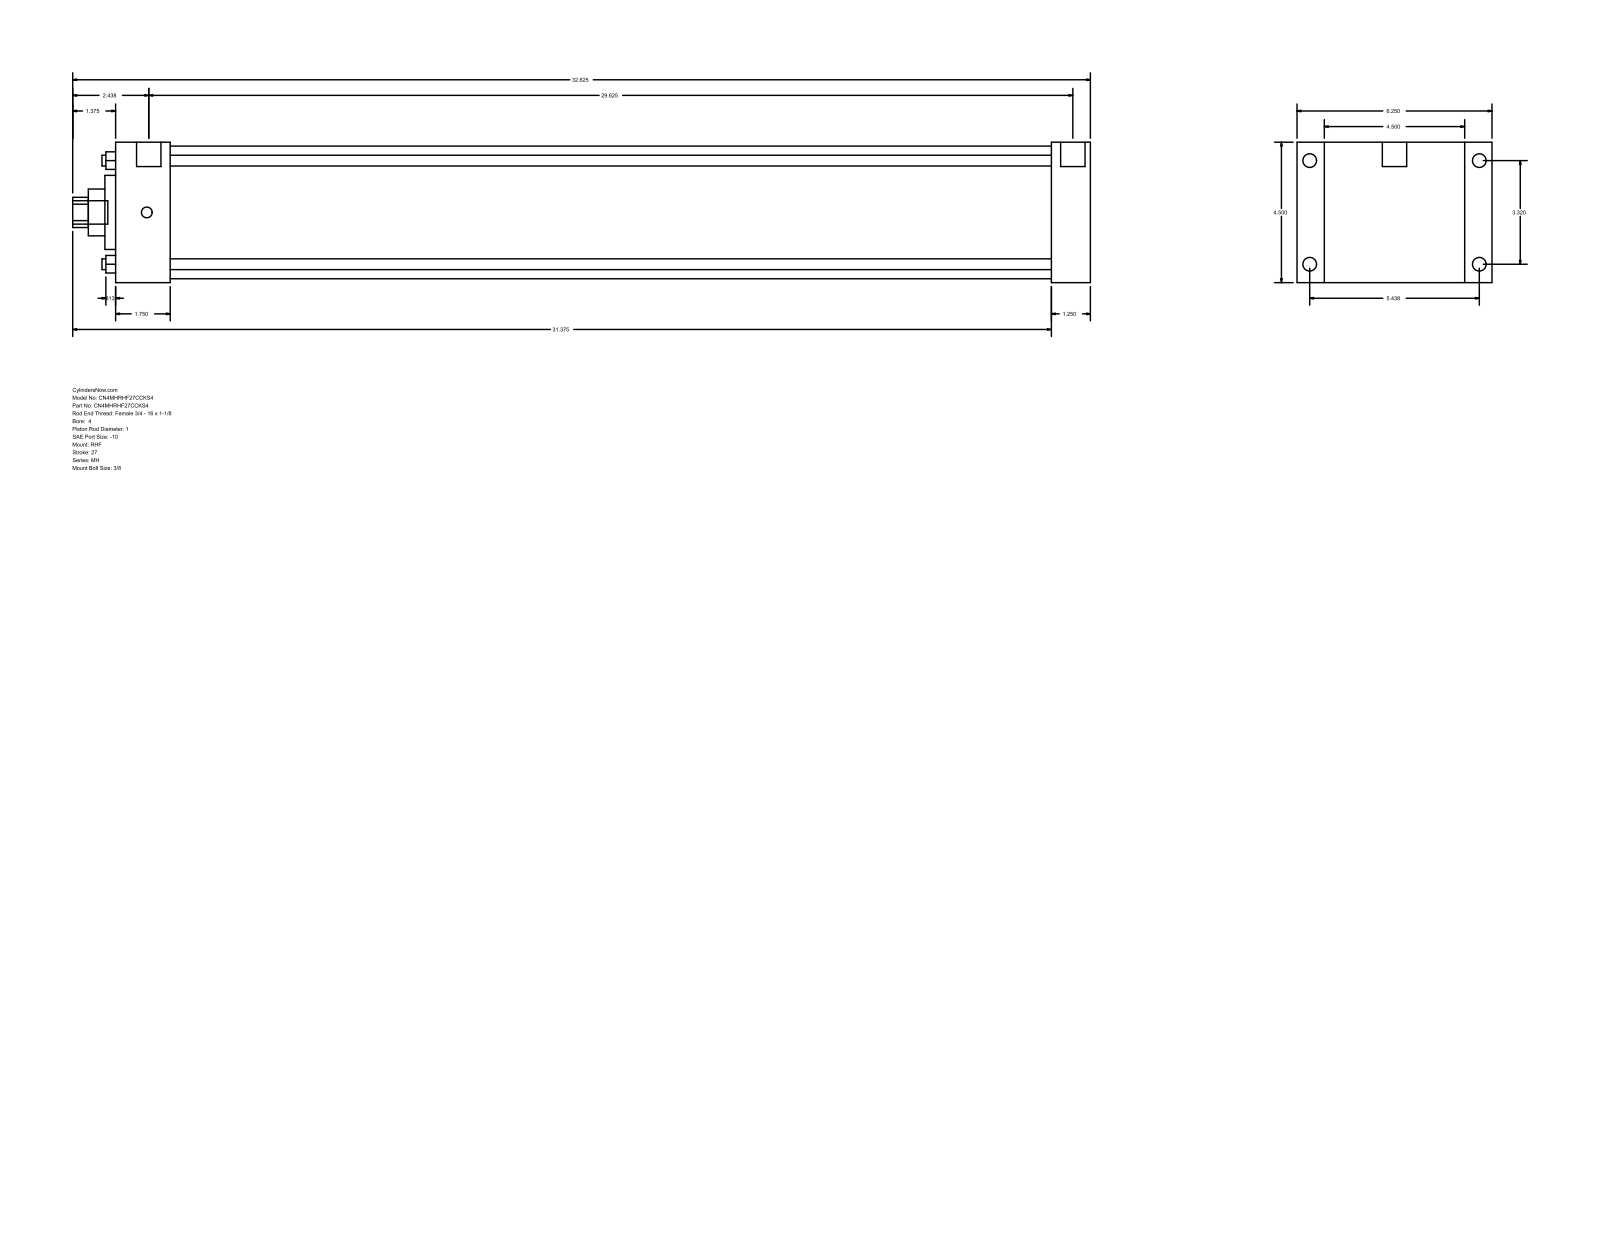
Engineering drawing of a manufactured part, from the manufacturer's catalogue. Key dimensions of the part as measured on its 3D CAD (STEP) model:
Part name (STEP PRODUCT): MH_RHF__0400_1
STEP written by: GSSL Pune (CONFIG_CONTROL_DESIGN)
Units: millimetres
Bodies: 0 solids, 90 faces (61 planar, 29 cylindrical, 0 other)
Overall size (bounding box): 828.67 × 158.75 × 114.3
Round holes (diameter × count): ⌀8.76 ×4, ⌀25.4 ×1, ⌀38.1 ×1, ⌀60.33 ×1, ⌀107.95 ×1
Round bosses / shafts (diameter × count): ⌀11.13 ×4, ⌀8.73 ×4, ⌀19.84 ×2, ⌀19.05 ×1
Partial cylindrical surfaces — rounded edges, fillets, slot ends (radius × count): R12.29 ×1
Main face-to-face distances: 114.3, 793.75, 762, 31.75, 22.23, 136.53, 44.46, 717.54, 749.29, 158.76
Hole centre spacings: 59.62, 84.32, 119.25
